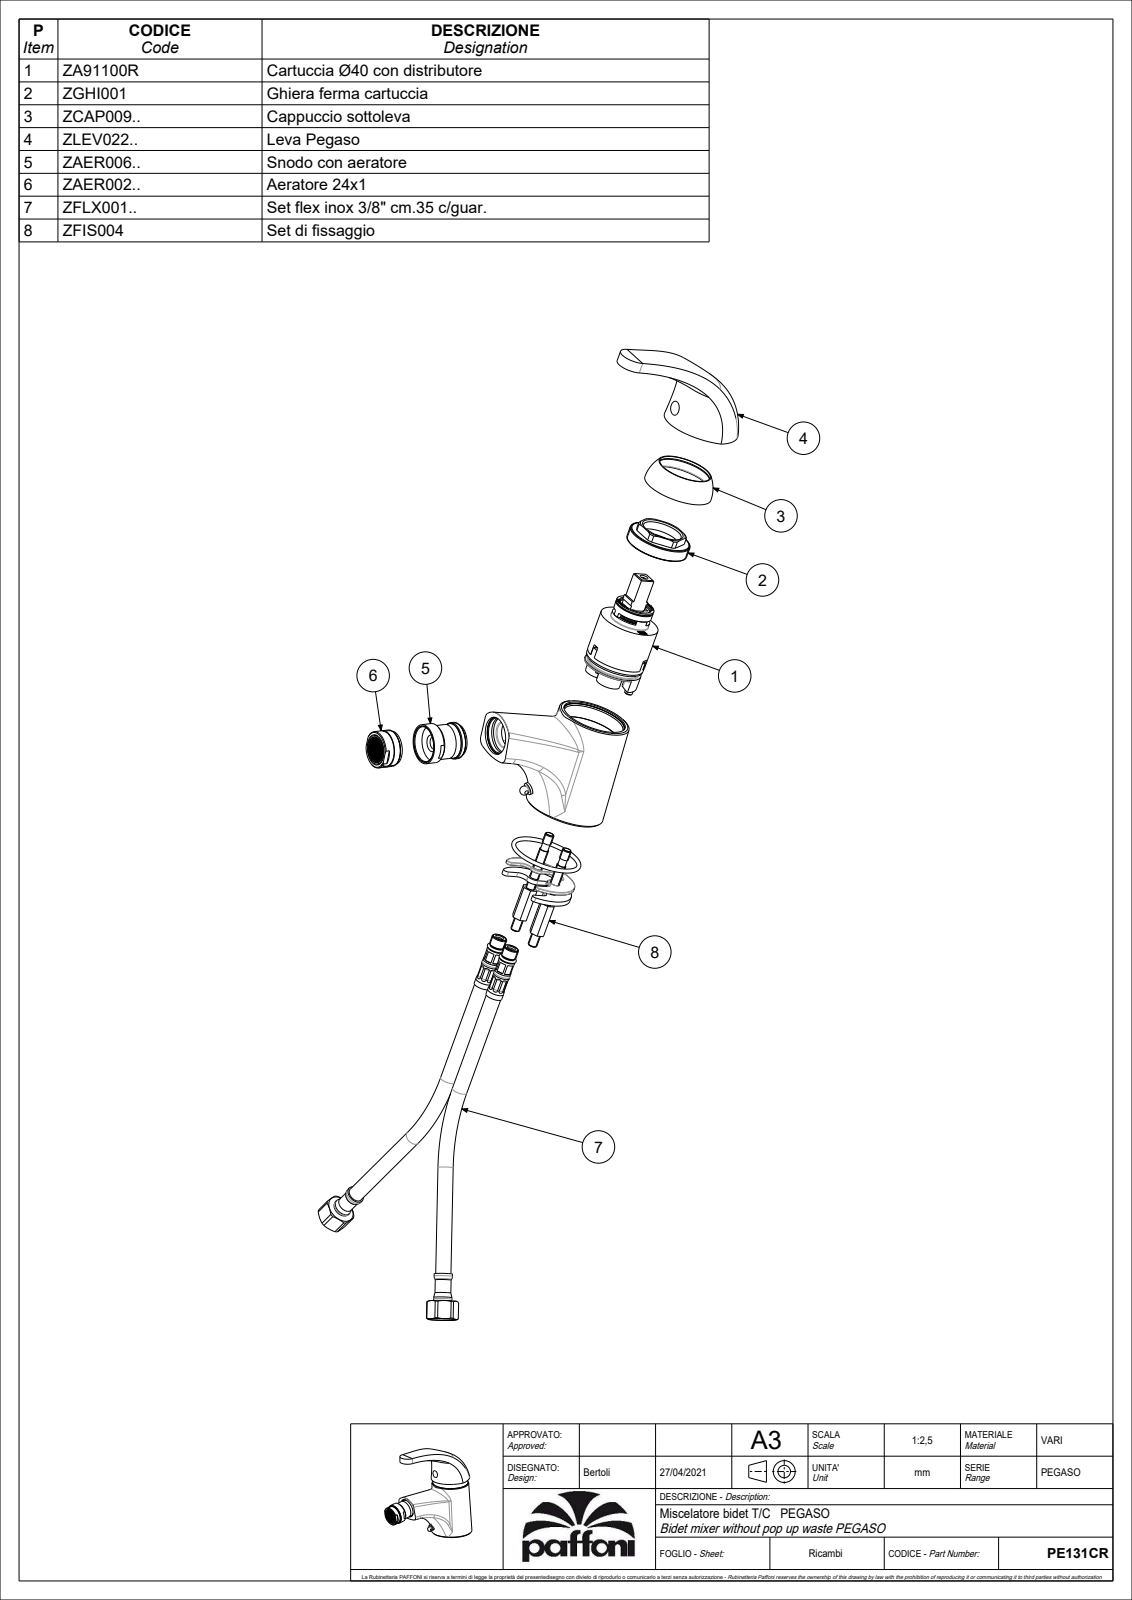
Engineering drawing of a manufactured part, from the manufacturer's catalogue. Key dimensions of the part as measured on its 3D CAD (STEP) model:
Part name (STEP PRODUCT): PE131CR_SW0001
STEP written by: CREO PARAMETRIC BY PTC INC, 2022124 (CONFIG_CONTROL_DESIGN)
Units: millimetres
Bodies: 1 solid, 369 faces (113 planar, 109 cylindrical, 147 other)
Overall size (bounding box): 133.25 × 122.07 × 52.85
Volume: 126 657 mm³ · Surface area: 64 656 mm²
Round holes (diameter × count): ⌀5.25 ×2, ⌀5.5 ×2, ⌀7 ×2, ⌀9 ×2, ⌀11 ×2, ⌀3.7 ×1, ⌀6 ×1, ⌀7.5 ×1, ⌀15.5 ×1, ⌀16 ×1, ⌀39.1 ×1, ⌀40.5 ×1
Round bosses / shafts (diameter × count): ⌀10 ×3, ⌀8 ×2, ⌀41.7 ×1, ⌀25.8 ×1, ⌀24 ×1, ⌀22.5 ×1, ⌀18.8 ×1, ⌀5 ×1
Partial cylindrical surfaces — rounded edges, fillets, slot ends (radius × count): R1 ×8, R2 ×5, R5 ×3, R9 ×2, R3.9 ×1, R15.3 ×1, R18.75 ×1, R19 ×1
Main face-to-face distances: 3.7, 13, 21.5, 2, 82.47, 60.97, 61, 3.5, 82.5, 17
Hole centre spacings: 0.71, 2.69, 8.6, 9.3, 10.26, 10.97, 12.08, 13.12
